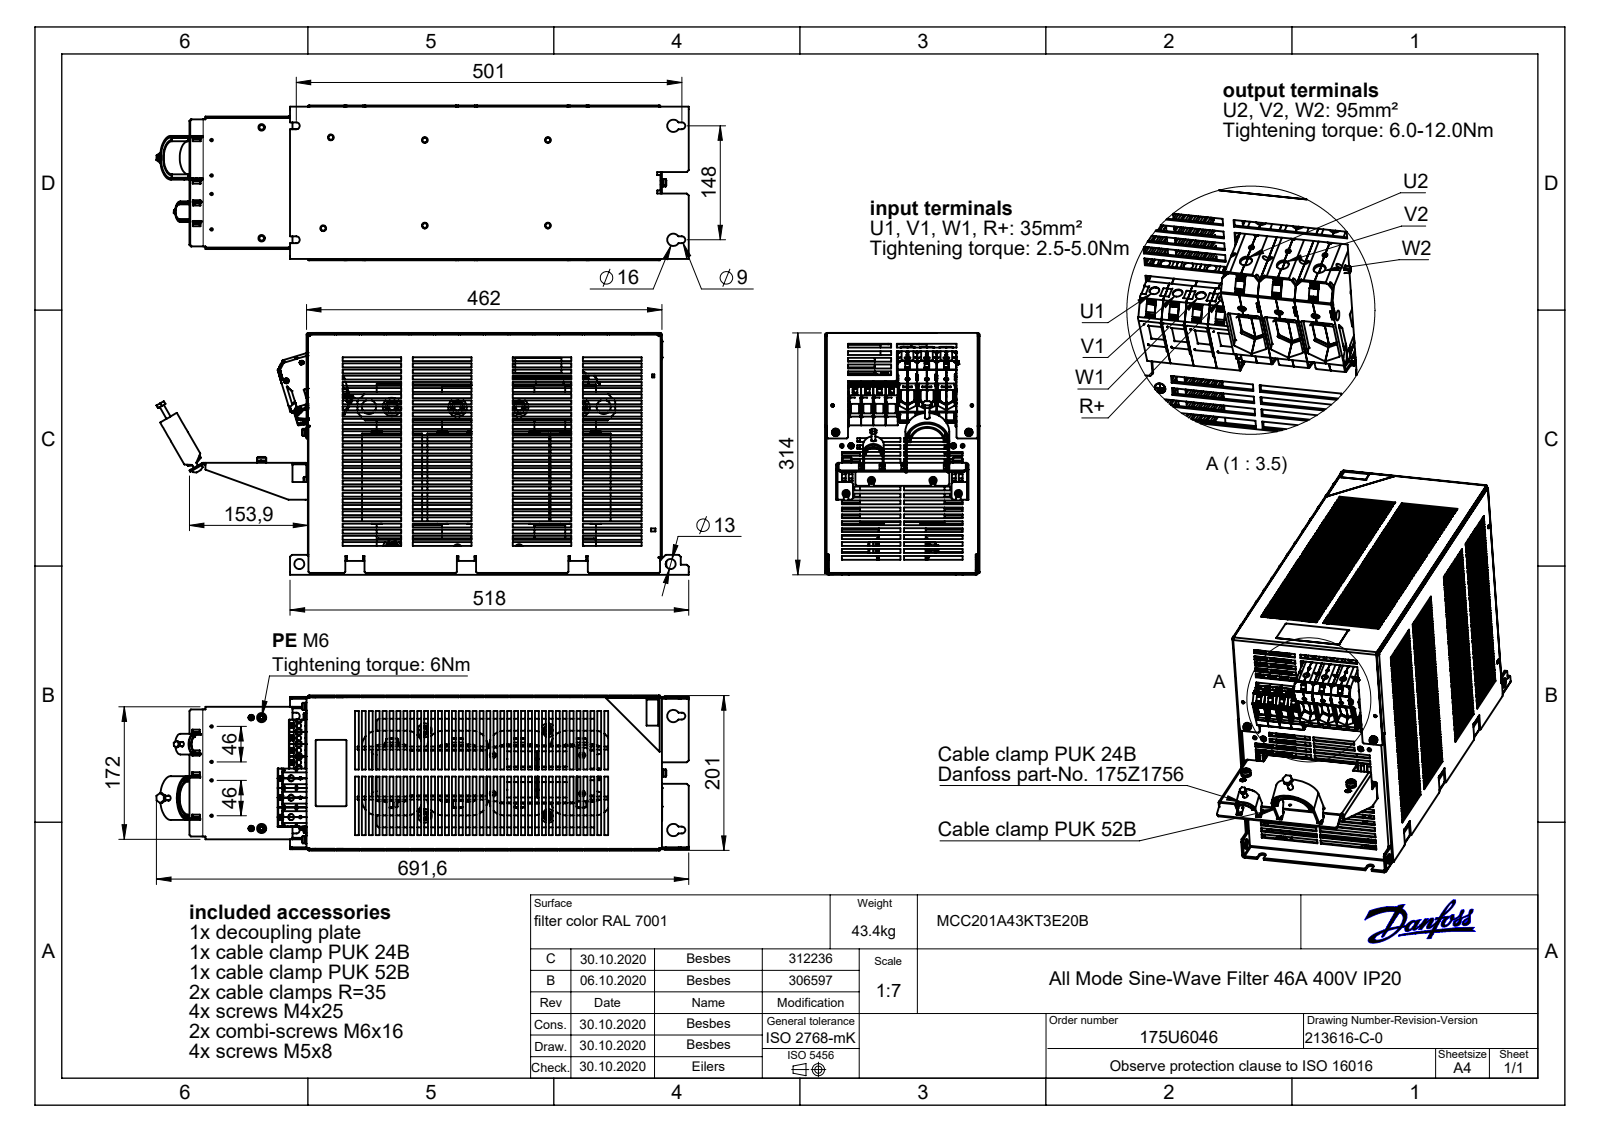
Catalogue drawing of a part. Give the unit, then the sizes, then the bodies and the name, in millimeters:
Units: millimetres
Overall size (bounding box): 691.62 × 314.1 × 201
Round holes (diameter × count): ⌀2.75 ×15, ⌀5 ×14, ⌀6.5 ×13, ⌀2.5 ×12, ⌀4.2 ×11, ⌀4.5 ×11, ⌀8 ×11, ⌀2.41 ×9, ⌀3.4 ×9, ⌀3.3 ×8, ⌀6.8 ×8, ⌀7.95 ×8
Round bosses / shafts (diameter × count): ⌀18 ×12, ⌀1 ×12, ⌀7 ×10, ⌀16 ×8, ⌀10 ×8, ⌀5 ×8, ⌀9.5 ×7, ⌀8 ×7
Partial cylindrical surfaces — rounded edges, fillets, slot ends (radius × count): R0.3 ×564, R0.5 ×209, R1 ×152, R10 ×32, R3 ×24, R5.5 ×22, R2 ×20, R0.25 ×18
Main face-to-face distances: 1.5, 129.5, 70, 199.5, 2.5, 71.5, 131, 59.5, 128, 68.5
Hole centre spacings: 25.2, 28.13, 15.9, 24.5, 29.63, 80, 25, 27.69
Volume: 7 442 000 mm³ · Surface area: 2 655 000 mm²
Bodies: 163 solids, 13414 faces (7668 planar, 3718 cylindrical, 2028 other)
Part name (STEP PRODUCT): Kombischraube-Tx M5x10 ISO 14583 4.8 vz_Kombischraube-Tx M5x10 ISO 14583 4.8 vz; U-Scheibe M10 DIN125 140 HV vz_U-Scheibe M10 DIN125 140 HV vz; 139758; U-Scheibe M6 DIN 9021 140 HV vz_U-Scheibe M6 DIN 9021 140 HV vz (+8 more)
STEP written by: SolidWorks 2018 (AUTOMOTIVE_DESIGN)
